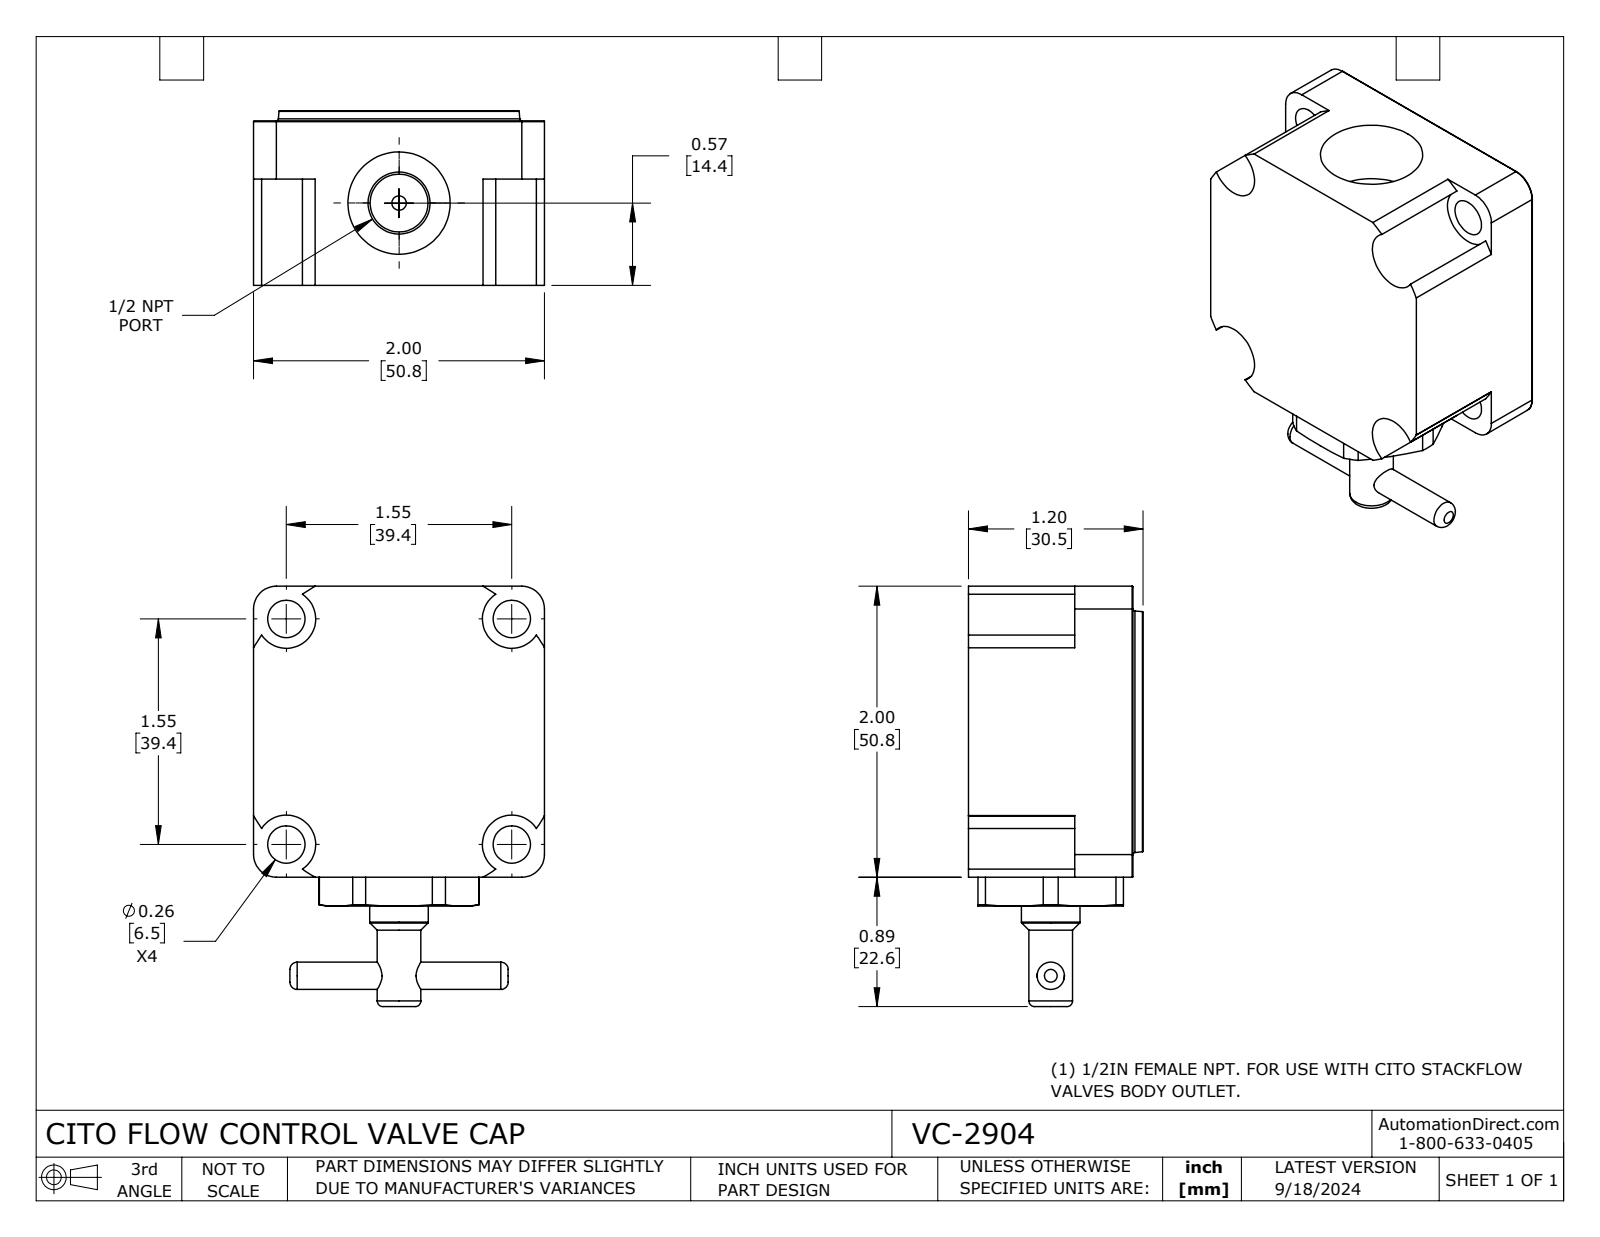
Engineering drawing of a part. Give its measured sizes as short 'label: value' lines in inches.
name: VC-2904
written by: SolidWorks 2023 (CONFIG_CONTROL_DESIGN)
unit: in
bodies: 4 solids, 284 faces (40 planar, 130 cylindrical, 114 other)
size: 2.889 × 2 × 1.2
volume: 3.43 in³; area: 32.2 in²
holes: 4× ⌀0.257, 1× ⌀0.188, 1× ⌀0.402, 1× ⌀0.426, 1× ⌀0.461, 1× ⌀0.638, 1× ⌀0.703, 1× ⌀0.911
bosses: 1× ⌀1.003, 1× ⌀0.977, 1× ⌀0.91, 1× ⌀0.496, 1× ⌀0.493, 1× ⌀0.462, 1× ⌀0.403, 1× ⌀0.3
rounds: 5× R0.005, 4× R0.156, 4× R0.202, 4× R0.25, 1× R0.265, 1× R0.519, 1× R0.55, 1× R1.155
face distances: 2, 1.13, 0.07, 1.2, 1, 0.13, 0.4, 1.07, 0.199, 2.199
hole spacings: 1.55, 1.55, 2.192, 2.193
